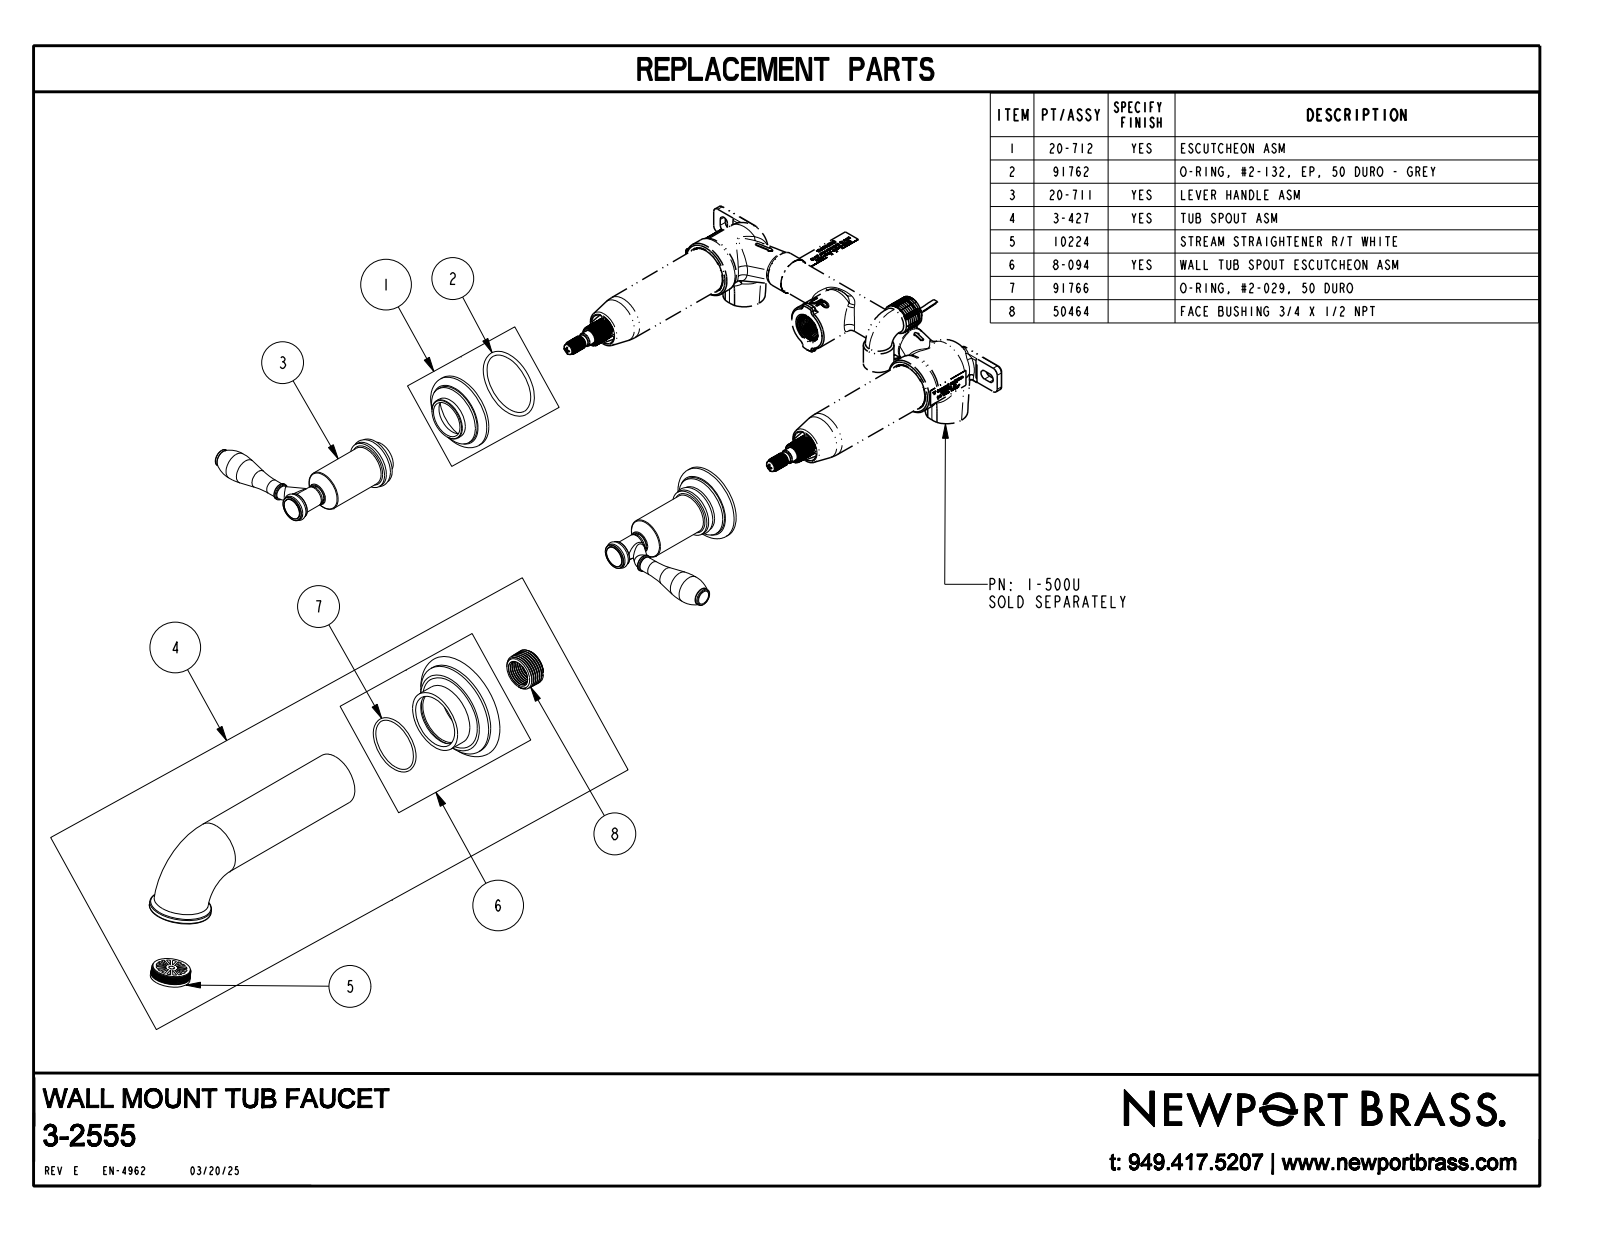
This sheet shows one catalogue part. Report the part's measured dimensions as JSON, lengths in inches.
{"part_name": "3-2555_SW0001", "step_written_by": "CREO PARAMETRIC BY PTC INC, 2018400 (AUTOMOTIVE_DESIGN)", "units": "inches", "bodies": {"solids": 3, "faces": 207, "planar": 25, "cylindrical": 66, "other": 116}, "overall_size": [14.175, 8.574, 6.911], "volume_in3": 23.1, "surface_area_in2": 96.28, "round_bosses_or_shafts": [[2.11, 2], [1.7, 2], [1.33, 2], [1.12, 2], [0.714, 2], [0.6, 2], [0.57, 2], [0.42, 2]], "face_to_face_distances": [0.03, 0.02, 0.45, 0.25, 0.75, 1.03, 1.02, 1, 0.48, 0.47]}
